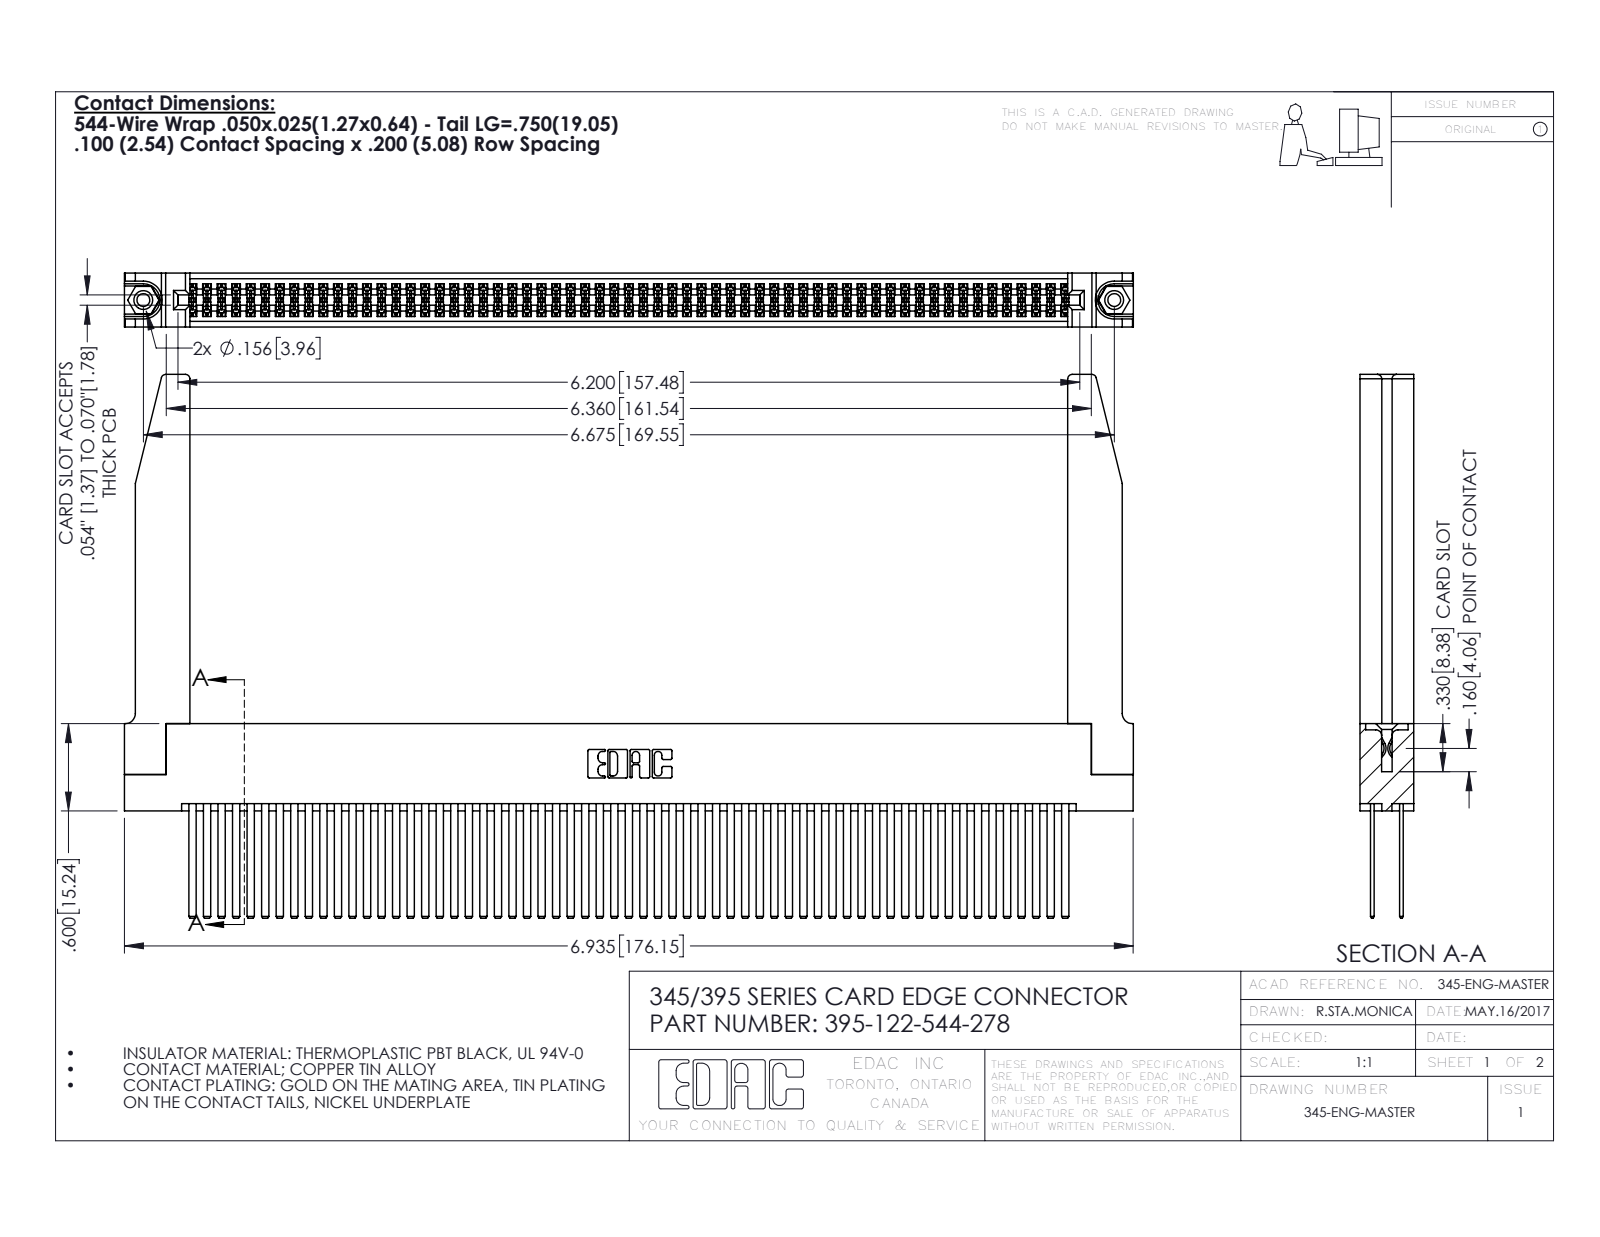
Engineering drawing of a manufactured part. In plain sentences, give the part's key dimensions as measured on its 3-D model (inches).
The part is named "345-250-001_345-250-001-102; 395-122-544-278; 345-220-078_345-220-078; 345 Part_Flush Mounting Lugs - 0.156 Dia-TH (+1 more)". Its 3-D file was written by "SolidWorks 2016 (CONFIG_CONTROL_DESIGN)". It is 127 solids with 5728 faces: 3760 planar, 1916 cylindrical and 52 other. Overall it measures 6.936 by 3.737 by 0.37 inches. Its volume is 1.634 cubic inches and its surface area 62.47 square inches. Round holes: 2 of diameter 0.089, 2 of diameter 0.125, 2 of diameter 0.156, 1 of diameter 0.064. Round bosses or shafts: 2 of diameter 0.155. Partial cylindrical surfaces (rounded edges, fillets, slot ends): 183 of radius 0.006, 22 of radius 0.01, 8 of radius 0.03, 6 of radius 0.007, 6 of radius 0.031, 3 of radius 0.026, 2 of radius 0.014, 2 of radius 0.019. The main face-to-face distances are 0.072, 0.298, 0.2, 0.098, 0.272, 0.025, 0.37, 0.225, 0.175, 0.148. The hole center spacings are 0.27, 6.439, 6.675.
